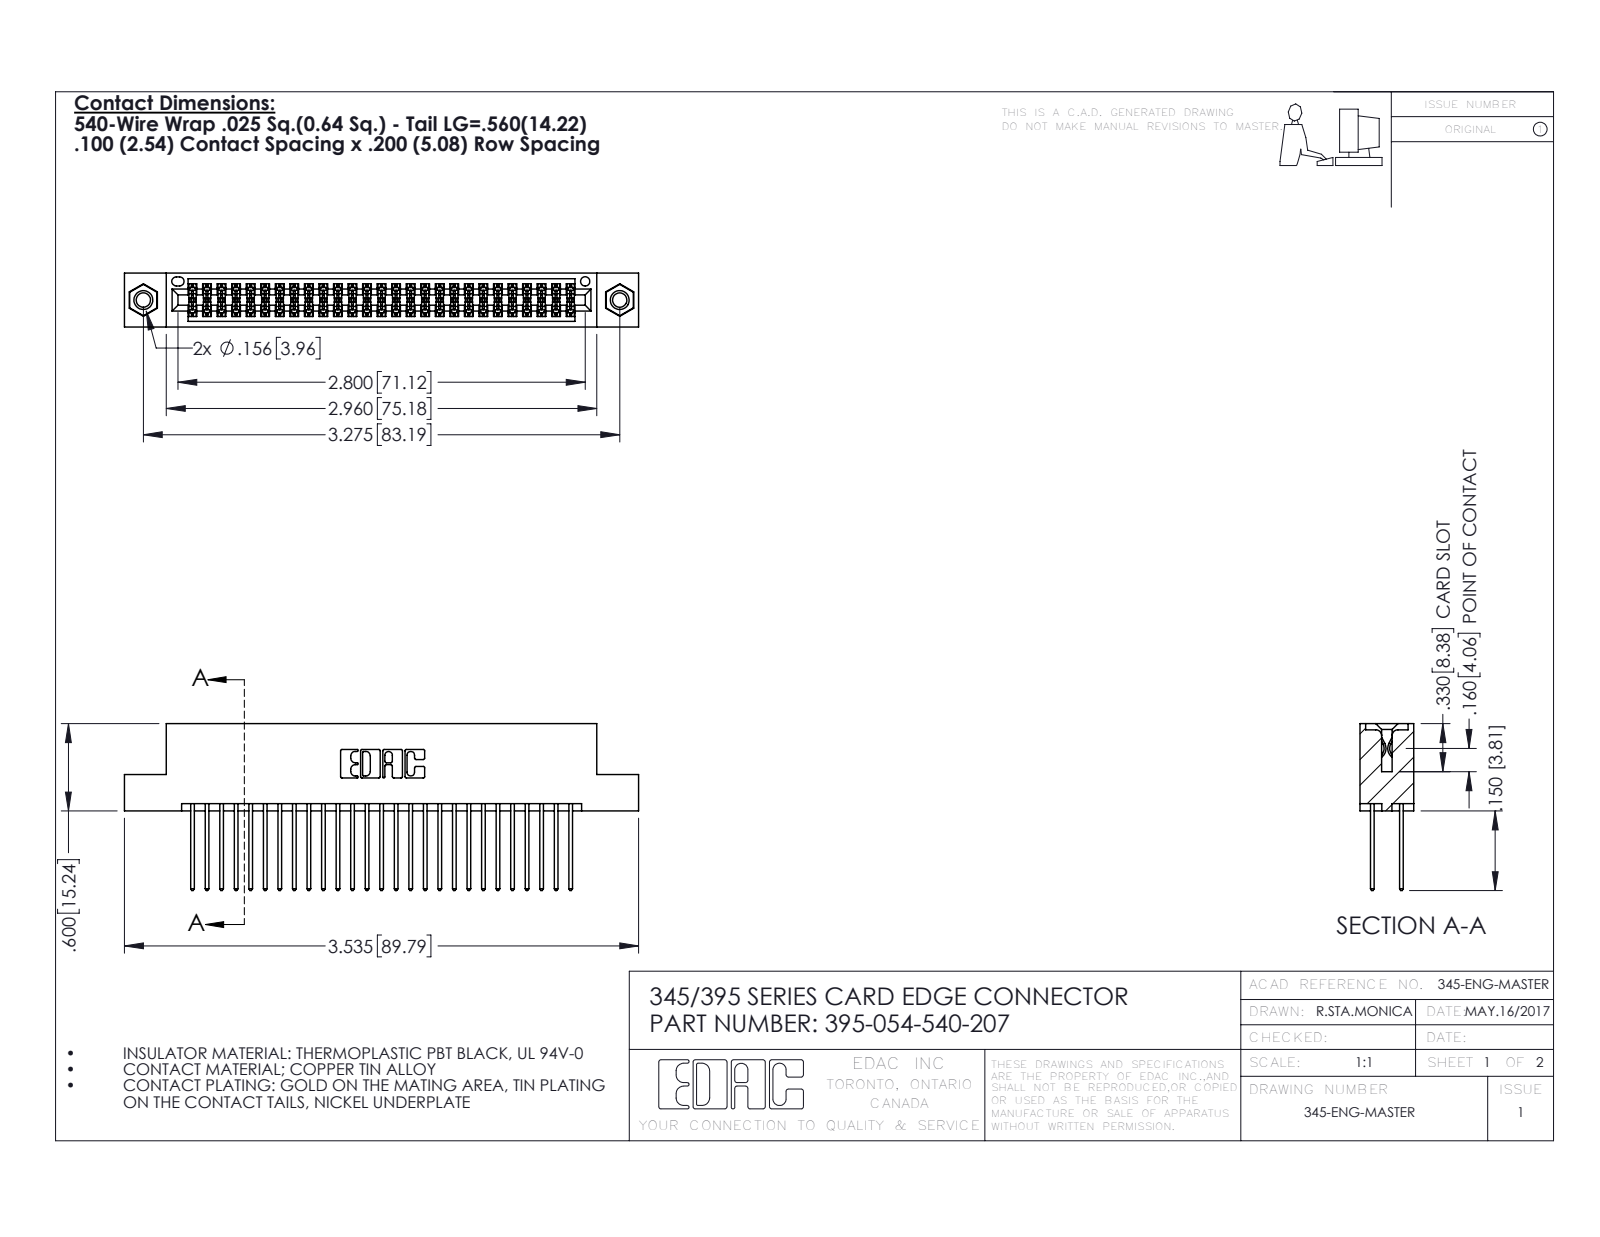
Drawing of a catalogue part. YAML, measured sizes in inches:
part_name: "345-292-001_345-293-140; 395-054-540-207; 345-250-001_345-250-005-103; 345 Part_Flush Mounting Lugs - 0.156 Dia-TI"
step_written_by: "SolidWorks 2016 (CONFIG_CONTROL_DESIGN)"
units: inches
bodies: {solids: 57, faces: 2886, planar: 1894, cylindrical: 976, other: 16}
overall_size: [3.535, 1.147, 0.37]
volume: 0.535
surface_area: 21.17
round_holes:
  - {diameter: 0.098, count: 2}
  - {diameter: 0.125, count: 2}
  - {diameter: 0.156, count: 2}
  - {diameter: 0.064, count: 1}
round_bosses_or_shafts:
  - {diameter: 0.155, count: 2}
partial_cylinders:
  - {radius: 0.006, count: 81}
  - {radius: 0.01, count: 54}
  - {radius: 0.01, count: 22}
  - {radius: 0.007, count: 6}
  - {radius: 0.031, count: 6}
  - {radius: 0.026, count: 3}
  - {radius: 0.014, count: 2}
  - {radius: 0.019, count: 2}
face_to_face_distances: [0.072, 0.298, 0.2, 0.098, 0.272, 0.025, 0.37, 0.225, 0.175, 0.149]
hole_center_spacings: [0.27, 3.04, 3.275]
